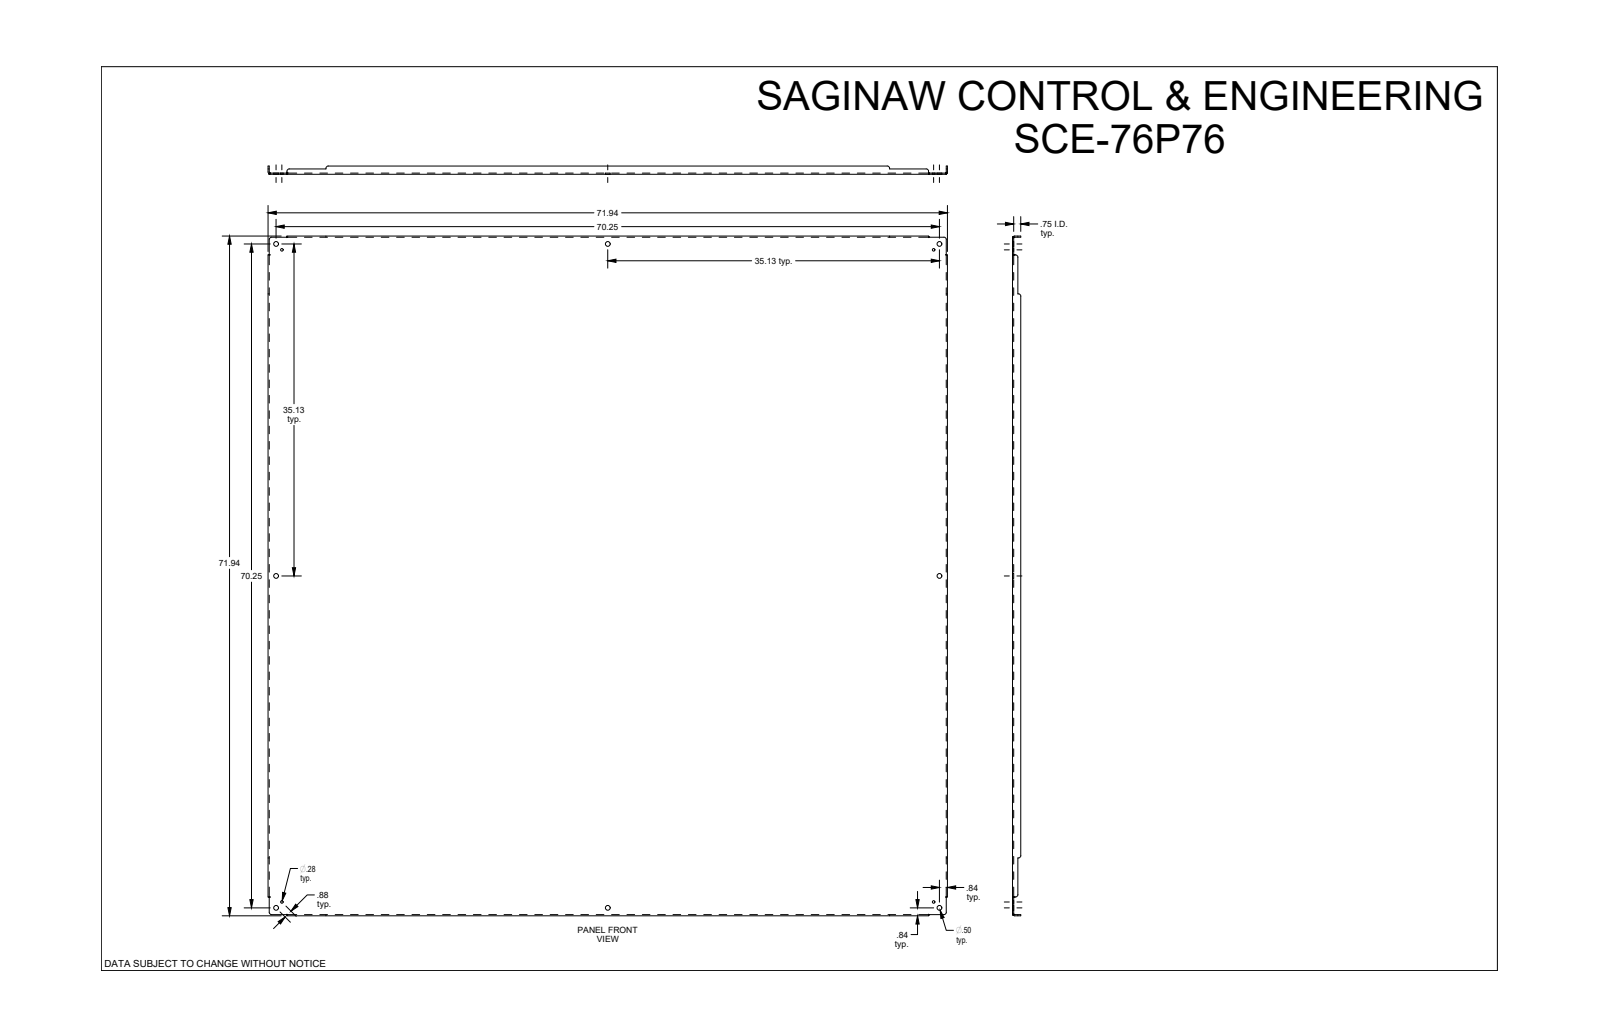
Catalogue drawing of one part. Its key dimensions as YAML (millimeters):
part_name: "SCE-76P76"
step_written_by: "SolidWorks 2019 (CONFIG_CONTROL_DESIGN)"
units: millimeters
bodies: {solids: 1, faces: 110, planar: 46, cylindrical: 40, other: 24}
overall_size: [1827.2, 1827.2, 22.2]
volume: 10950000
surface_area: 6921000
round_holes:
  - {diameter: 12.7, count: 8}
  - {diameter: 7.1, count: 4}
partial_cylinders:
  - {radius: 6.4, count: 12}
  - {radius: 2.8, count: 4}
  - {radius: 6, count: 4}
face_to_face_distances: [3.2, 3.2, 1824.1, 1820.8, 1827.2, 19.1, 22.2, 7.9, 11.1, 14.3]
hole_center_spacings: [876.6, 892.2, 1768.7, 1973.9, 1994.9, 1784.4, 22.2, 1261.7]
